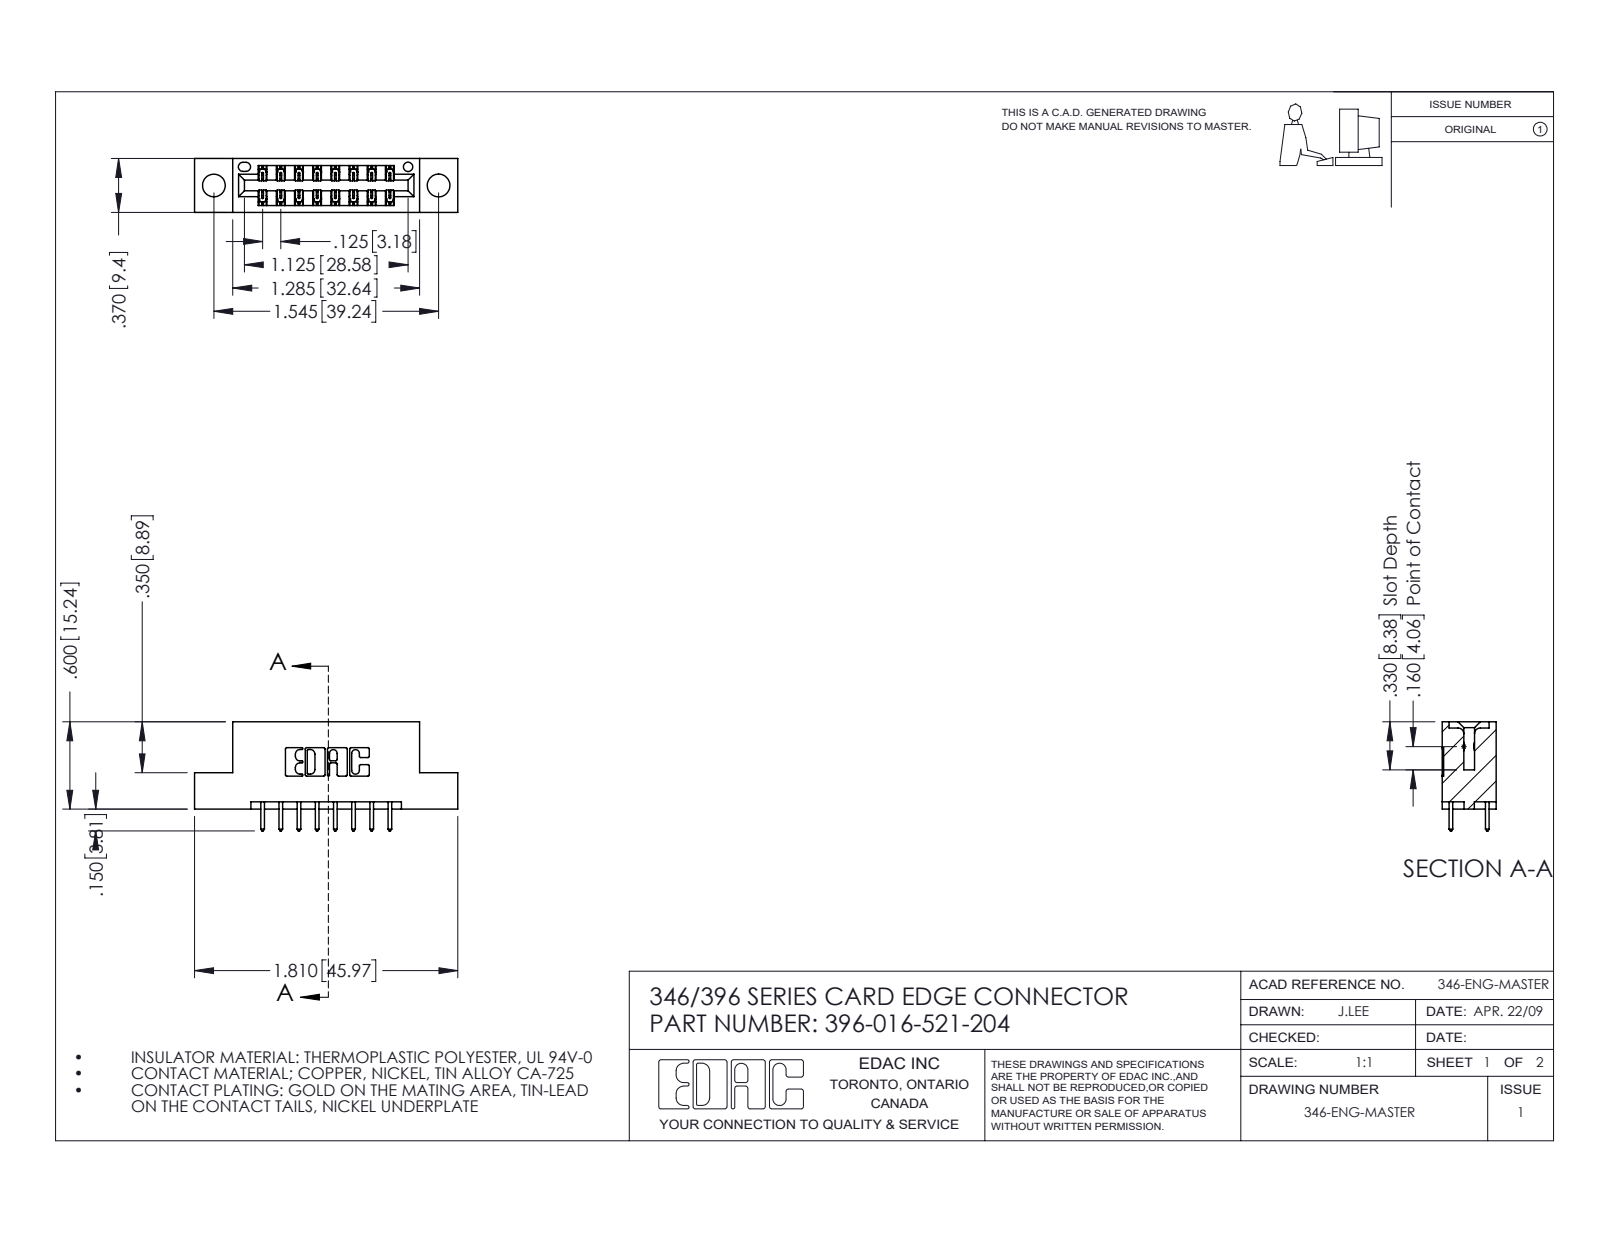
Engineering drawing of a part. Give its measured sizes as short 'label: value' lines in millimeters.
name: 345-292-001_345-293-121; 396-016-521-204; 346 Part_Flush Mounting Lugs - 0.156 Dia-TH
written by: SolidWorks 2016 (CONFIG_CONTROL_DESIGN)
unit: mm
bodies: 17 solids, 954 faces (636 planar, 318 cylindrical, 0 other)
size: 46 × 19.1 × 9.4
volume: 4 130 mm³; area: 4 905 mm²
holes: 2× ⌀4, 1× ⌀1.6
rounds: 24× R0.2, 22× R0.3, 16× R0.3, 6× R0.2, 6× R0.8, 3× R0.7, 2× R0.4, 2× R0.6
face distances: 6.4, 1.2, 8.2, 9.4, 1.8, 7.6, 0.6, 12.7, 7, 3.8
hole spacings: 6.2, 34.1, 39.2
